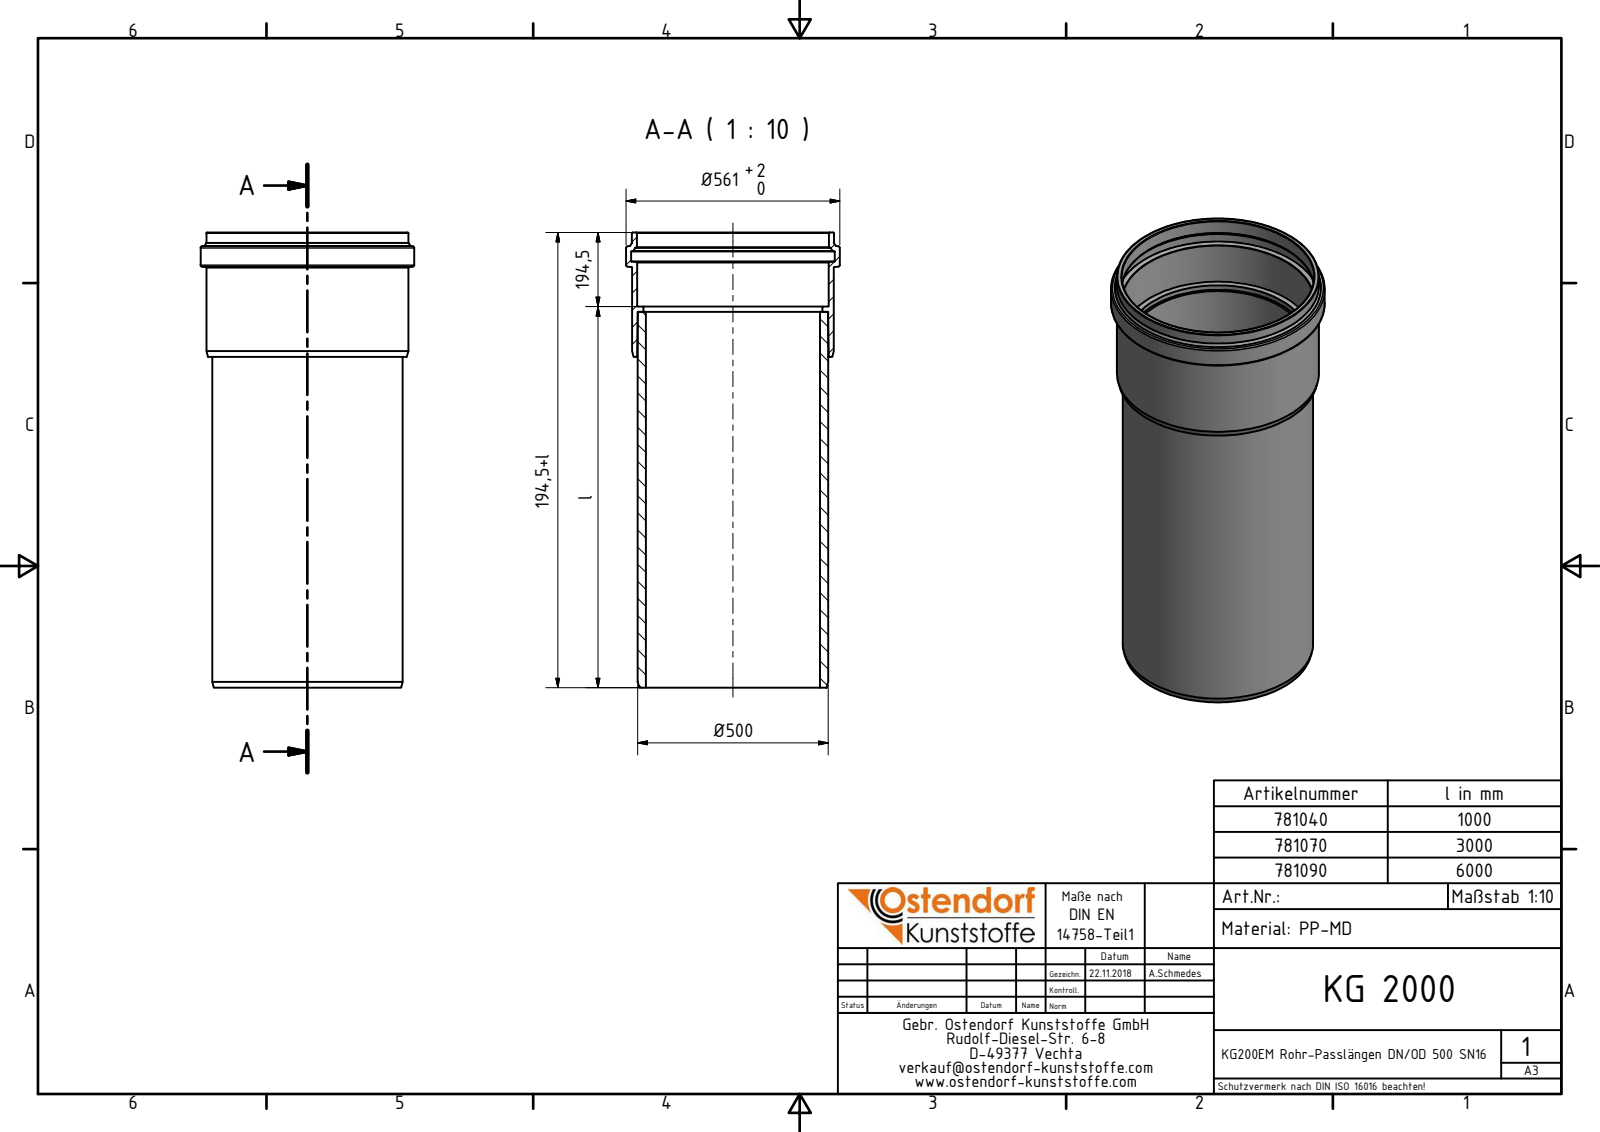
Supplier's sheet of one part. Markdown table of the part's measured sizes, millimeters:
| quantity | value |
| --- | --- |
| part name | 771040 KG2000EM Rohr-Passlängen DN_OD 500x1000 Teil1; 771040 KG2000EM Rohr-Passlängen DN_OD 500x1000 Teil2; 781040 KG2000EM Rohr-Passlängen DN_OD 500x1000 SN16 Zusammanbau |
| STEP written by | Autodesk Inventor 2016 (AUTOMOTIVE_DESIGN) |
| units | millimeters |
| bodies | 2 solids, 39 faces (6 planar, 9 cylindrical, 24 other) |
| overall size | 1194.5 × 561 × 561 |
| volume | 39 710 000 mm³ |
| surface area | 4 245 000 mm² |
| round holes (diameter × count) | 457.4 × 1, 470 × 1, 503.5 × 1, 504.5 × 1, 535 × 1 |
| round bosses / shafts (diameter × count) | 561 × 1, 530.5 × 1, 530 × 1, 500 × 1 |
| main face-to-face distances | 986, 14, 1000, 194.5, 208.5, 1194.5, 326.5, 132, 118, 868 |
